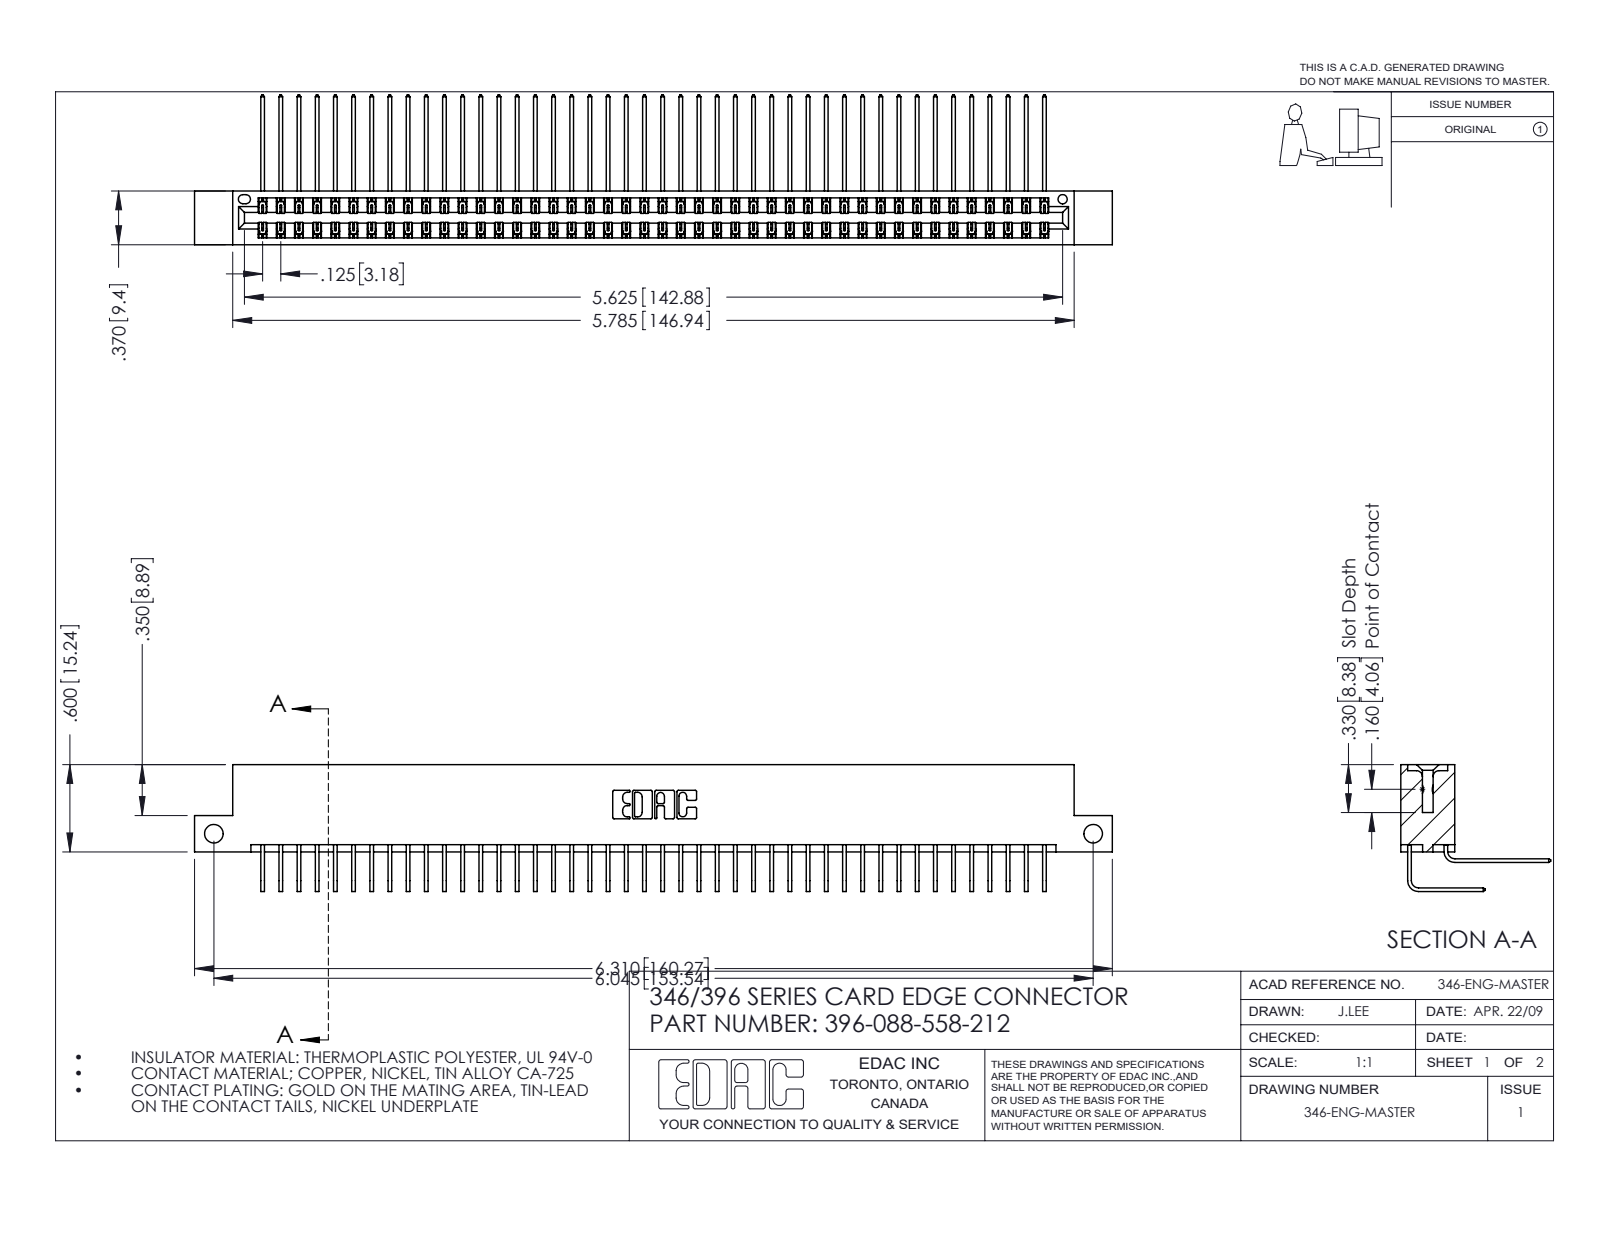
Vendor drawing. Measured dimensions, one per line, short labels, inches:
name: 345-292-001_558 559 Tail - 1; 396-088-558-212; 345-292-001_558 Tail - 2; 346 Part_Flush Mounting Lugs - Side Mount
written by: SolidWorks 2016 (CONFIG_CONTROL_DESIGN)
unit: in
bodies: 89 solids, 4874 faces (3332 planar, 1542 cylindrical, 0 other)
size: 6.31 × 1.03 × 0.873
volume: 0.98 in³; area: 37.84 in²
holes: 2× ⌀0.128, 1× ⌀0.064
rounds: 132× R0.006, 22× R0.01, 6× R0.007, 6× R0.031, 3× R0.026, 2× R0.014, 2× R0.022, 2× R0.024
face distances: 0.322, 0.048, 0.025, 0.37, 0.25, 0.298, 0.072, 0.275, 0.148, 0.222
hole spacings: 6.045
